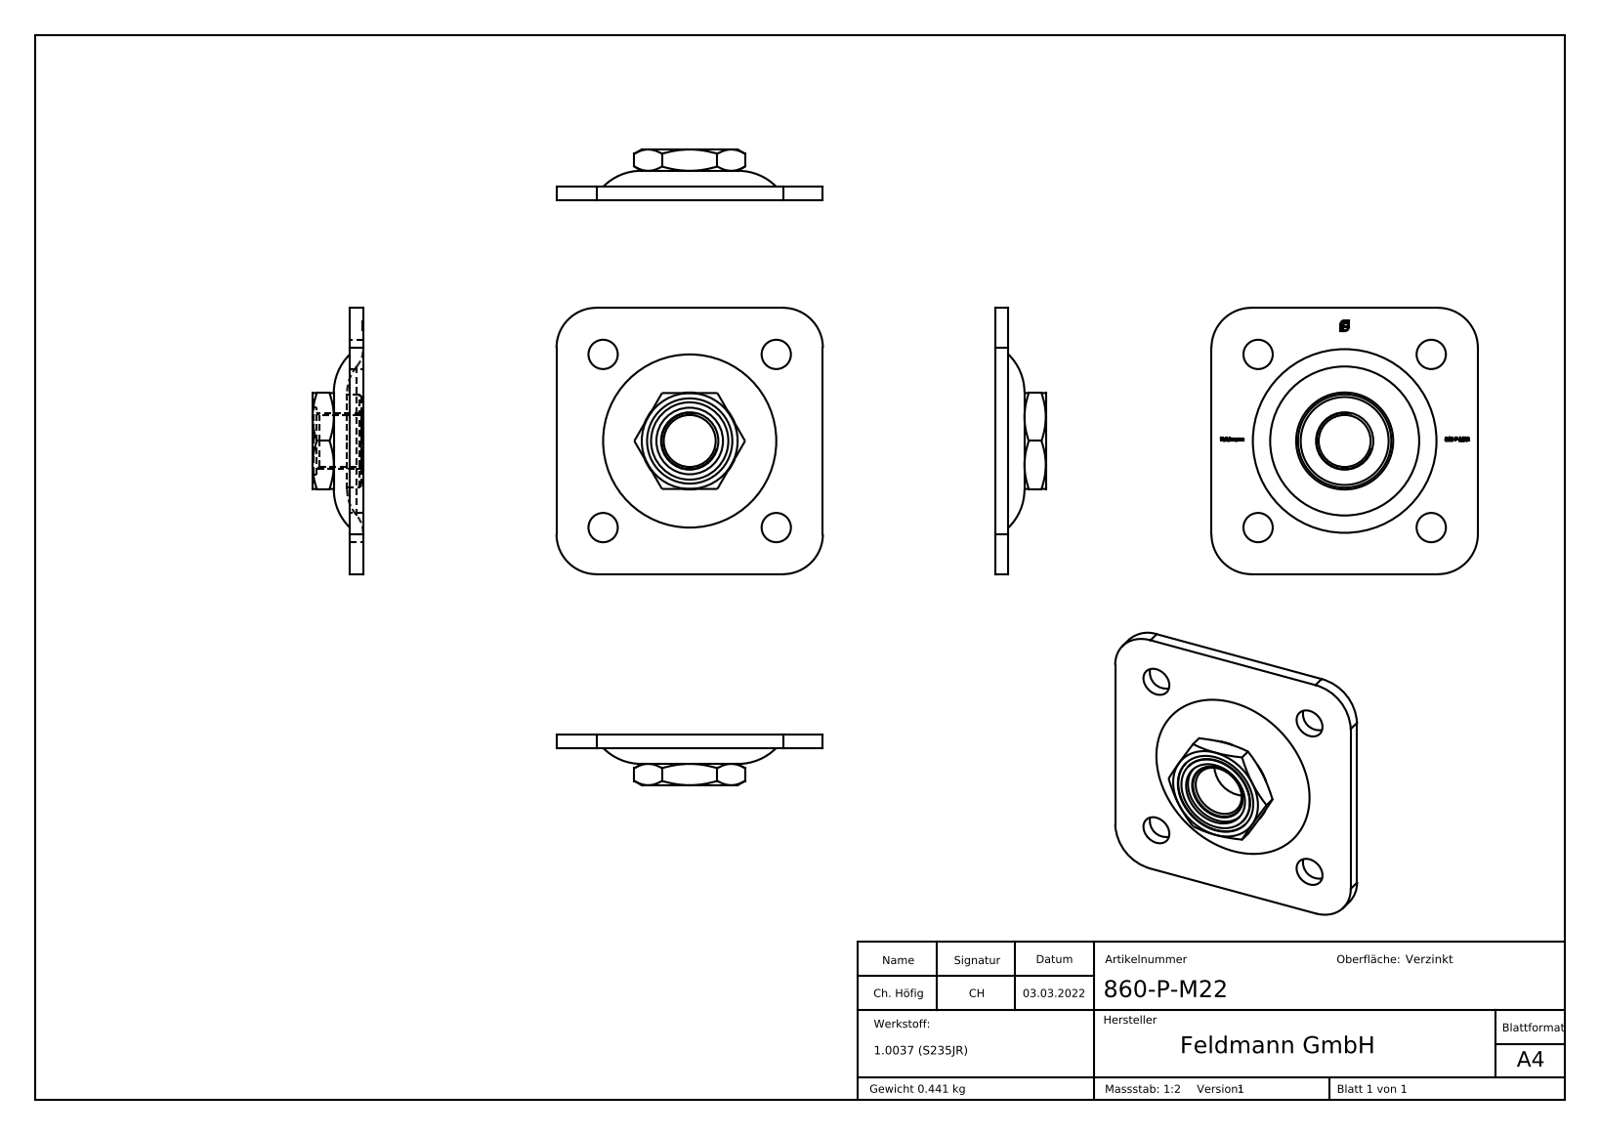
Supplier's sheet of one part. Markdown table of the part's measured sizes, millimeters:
| quantity | value |
| --- | --- |
| part name | 860-P-M22 |
| STEP written by | SolidWorks 2018 (CONFIG_CONTROL_DESIGN) |
| units | millimeters |
| bodies | 1 solid, 317 faces (165 planar, 13 cylindrical, 139 other) |
| overall size | 100 × 100 × 19 |
| volume | 56 508 mm³ |
| surface area | 24 165 mm² |
| round holes (diameter × count) | 11 × 4, 19.5 × 1, 25 × 1, 32 × 1 |
| round bosses / shafts (diameter × count) | 35 × 1, 29 × 1 |
| partial cylindrical surfaces (radius × count) | 15 × 4 |
| main face-to-face distances | 5, 100, 4.5, 0.5, 36, 19, 18.5, 14, 32, 68 |
| hole center spacings | 45.96, 65, 91.92 |
